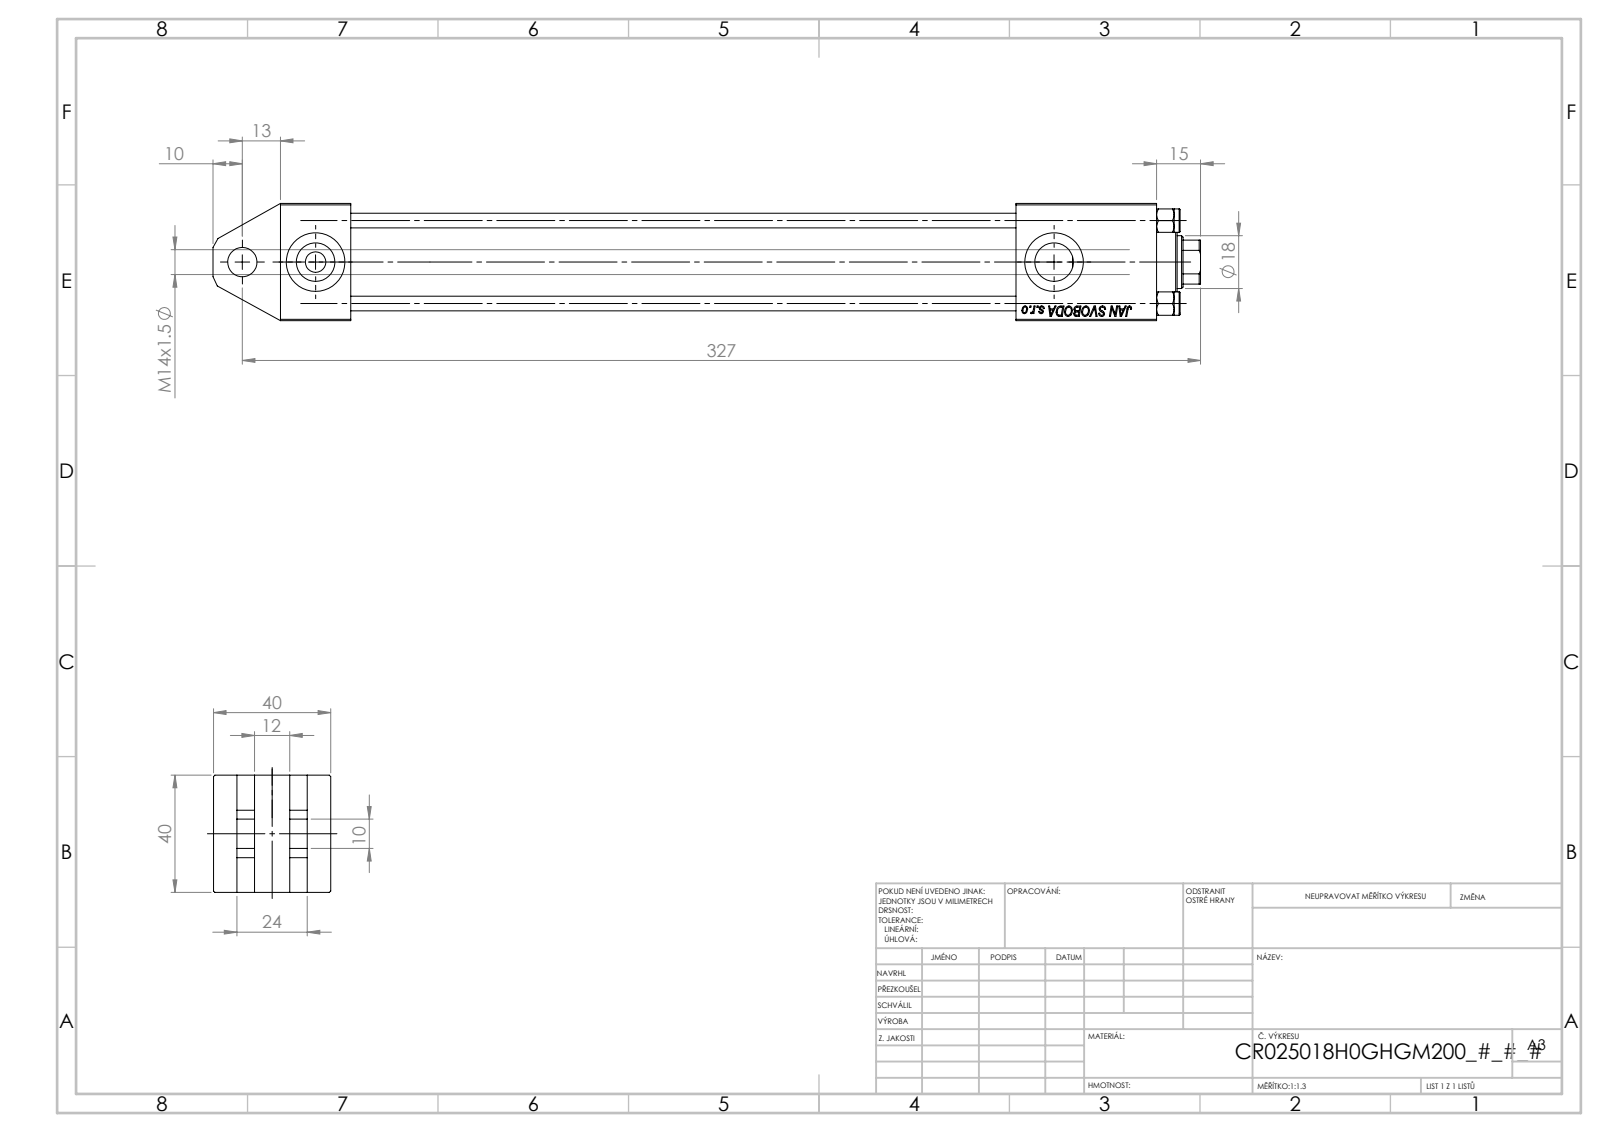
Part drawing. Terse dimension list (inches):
name: V215CR_H_Body; NUT_M5_H; V215CR_TYCINKA_H; V215CR_VCP_H (+1 more)
written by: SolidWorks 2019 (CONFIG_CONTROL_DESIGN)
unit: in
bodies: 11 solids, 1125 faces (516 planar, 81 cylindrical, 528 other)
size: 13.268 × 1.575 × 1.575
volume: 16.16 in³; area: 178.3 in²
holes: 4× ⌀0.197, 3× ⌀0.787, 2× ⌀0.276, 2× ⌀0.518, 1× ⌀0.335, 1× ⌀0.394, 1× ⌀0.709, 1× ⌀0.827, 1× ⌀0.984, 1× ⌀1.181
bosses: 4× ⌀0.315, 1× ⌀1.22
rounds: 1× R0.335
face distances: 1.575, 0.945, 0.315, 1.26, 0.236, 1.024, 0.551, 0.709, 9.882, 8.937
hole spacings: 0.788, 1.114, 1.576, 0.984, 9.921, 10.906
